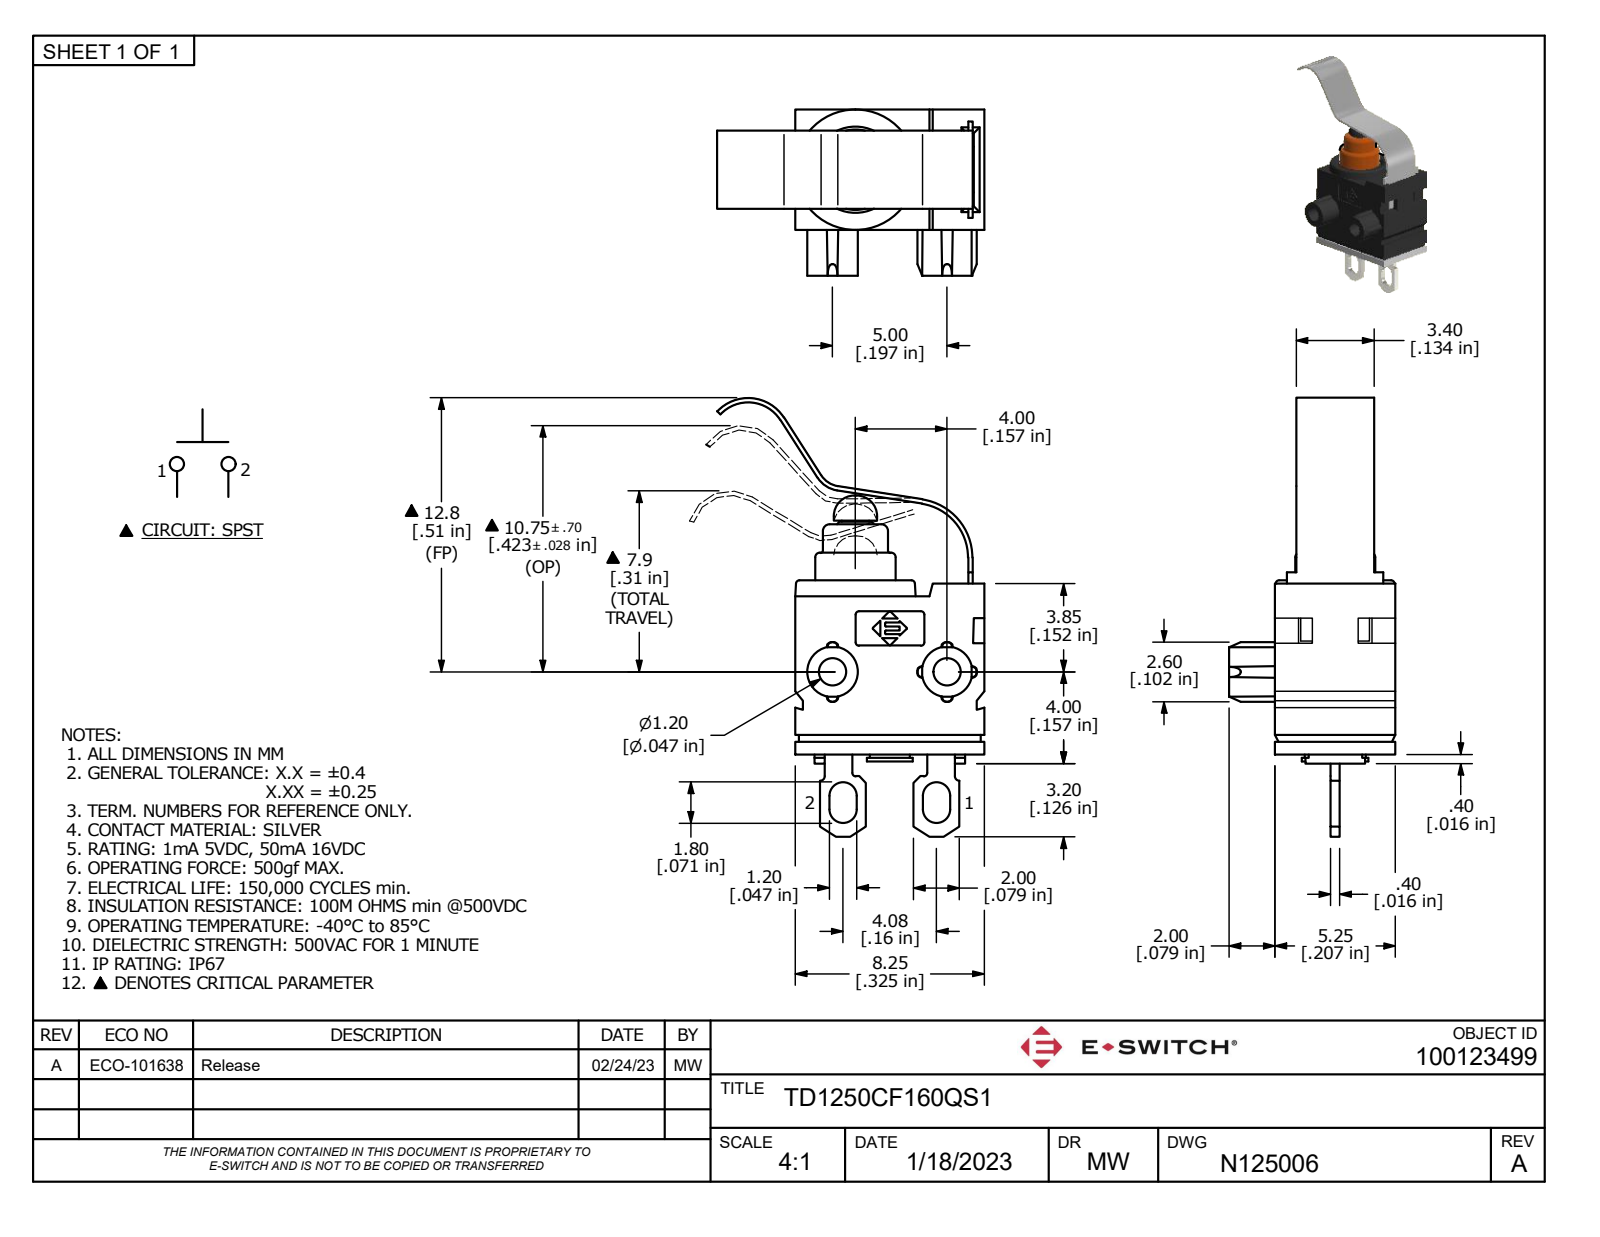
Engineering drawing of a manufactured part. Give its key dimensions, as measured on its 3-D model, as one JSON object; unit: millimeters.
{"part_name": "TD1250CF160QS1", "step_written_by": "Autodesk Inventor 2022 (AUTOMOTIVE_DESIGN)", "units": "millimeters", "bodies": {"solids": 1, "faces": 292, "planar": 223, "cylindrical": 57, "other": 12}, "overall_size": [19.16, 11.66, 7.25], "volume_mm3": 361, "surface_area_mm2": 589, "round_holes": [[1.2, 2], [4.65, 1]], "round_bosses_or_shafts": [[4.5, 1], [3.5, 1], [2.85, 1], [2.2, 1], [1.9, 1], [1.2, 1]], "partial_cylinders_radius": [[0.2, 14], [0.15, 8], [0.6, 4], [0.1, 3], [1.06, 1], [1.1, 1], [1.25, 1], [1.67, 1]], "face_to_face_distances": [5.24, 8.24, 0.55, 0.5, 2.42, 2.82, 6.9, 0.69, 7.55, 7.45], "hole_center_spacings": [5]}
